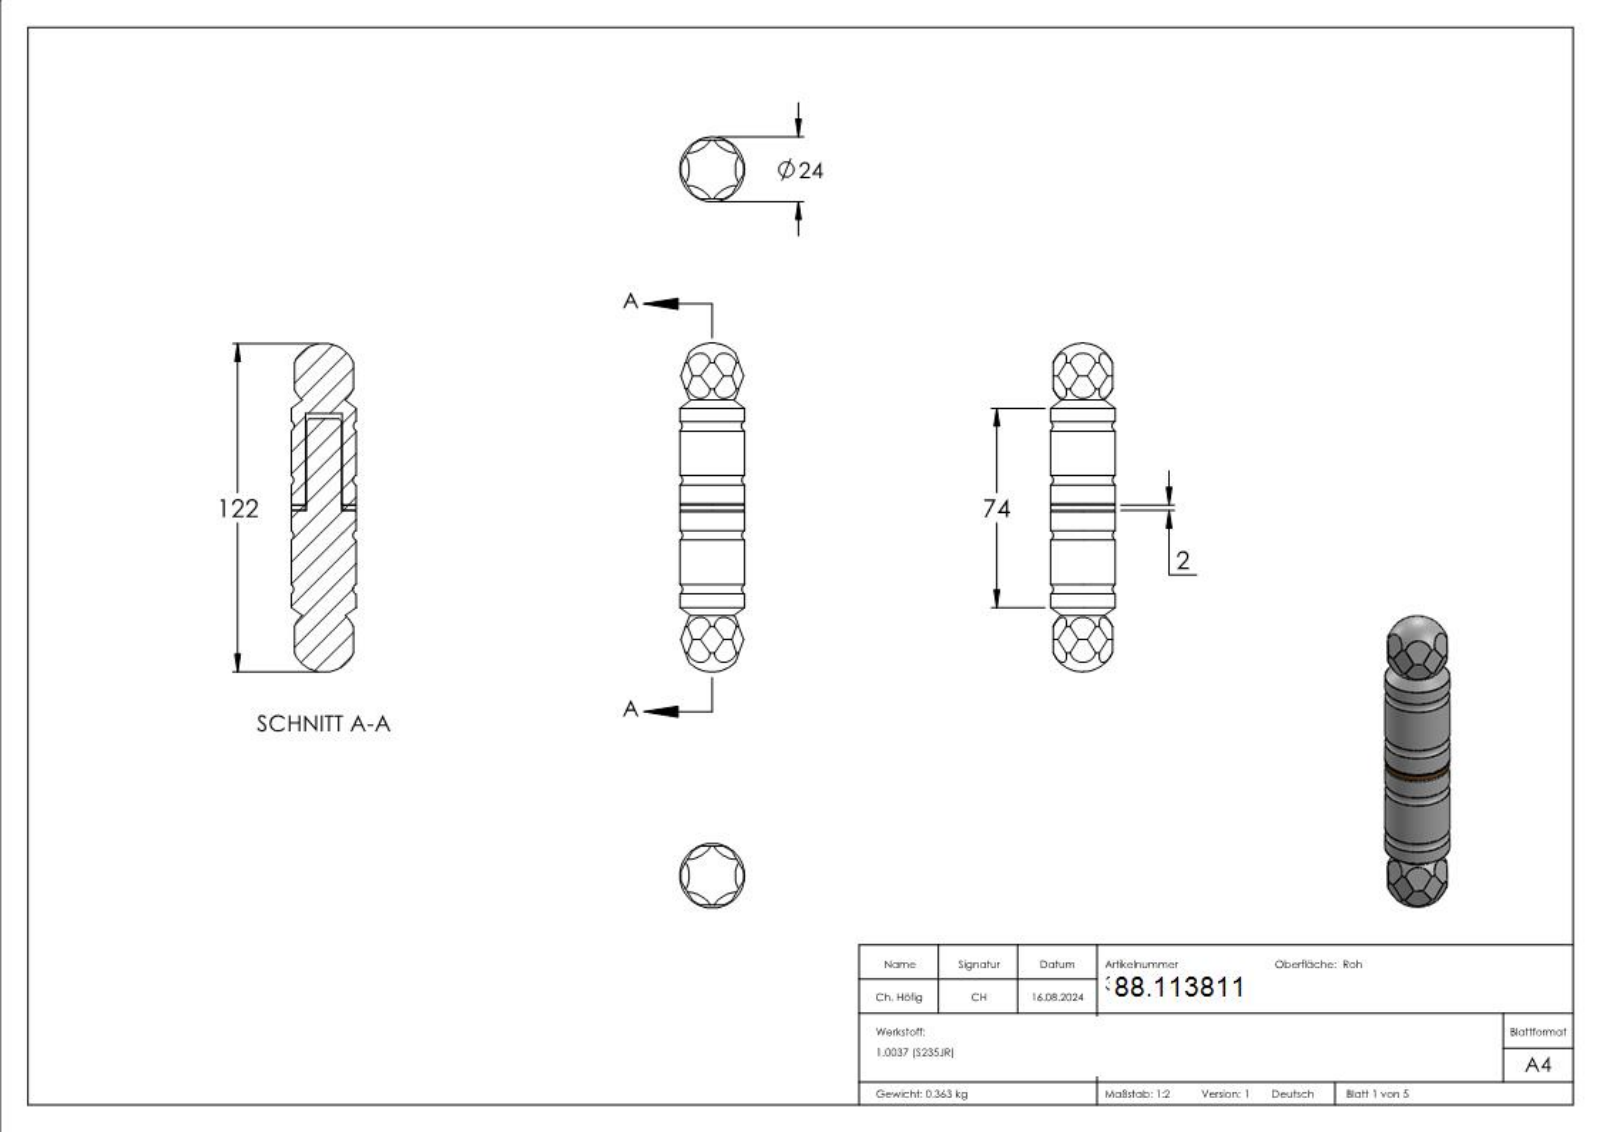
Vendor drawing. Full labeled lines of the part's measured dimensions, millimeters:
Part name (STEP PRODUCT): 3811; 3810 - 3811 - 3812 Teil1-3_3811 Teil2; 3810 - 3811 - 3812 Teil1-3_3811 Teil1; 3810 - 3811 - 3812 Teil1-3_3811 Teil3
STEP written by: SolidWorks 2018 (CONFIG_CONTROL_DESIGN)
Units: millimetres
Bodies: 3 solids, 274 faces (133 planar, 28 cylindrical, 113 other)
Overall size (bounding box): 122 × 24 × 24
Volume: 46 485 mm³ · Surface area: 13 723 mm²
Round holes (diameter × count): ⌀13.5 ×1, ⌀14 ×1
Round bosses / shafts (diameter × count): ⌀24 ×1, ⌀13 ×1
Partial cylindrical surfaces — rounded edges, fillets, slot ends (radius × count): R6.85 ×1
Main face-to-face distances: 21.9, 2, 33.52, 55.42, 11.62, 21.91, 33.51, 34, 36, 11.6
